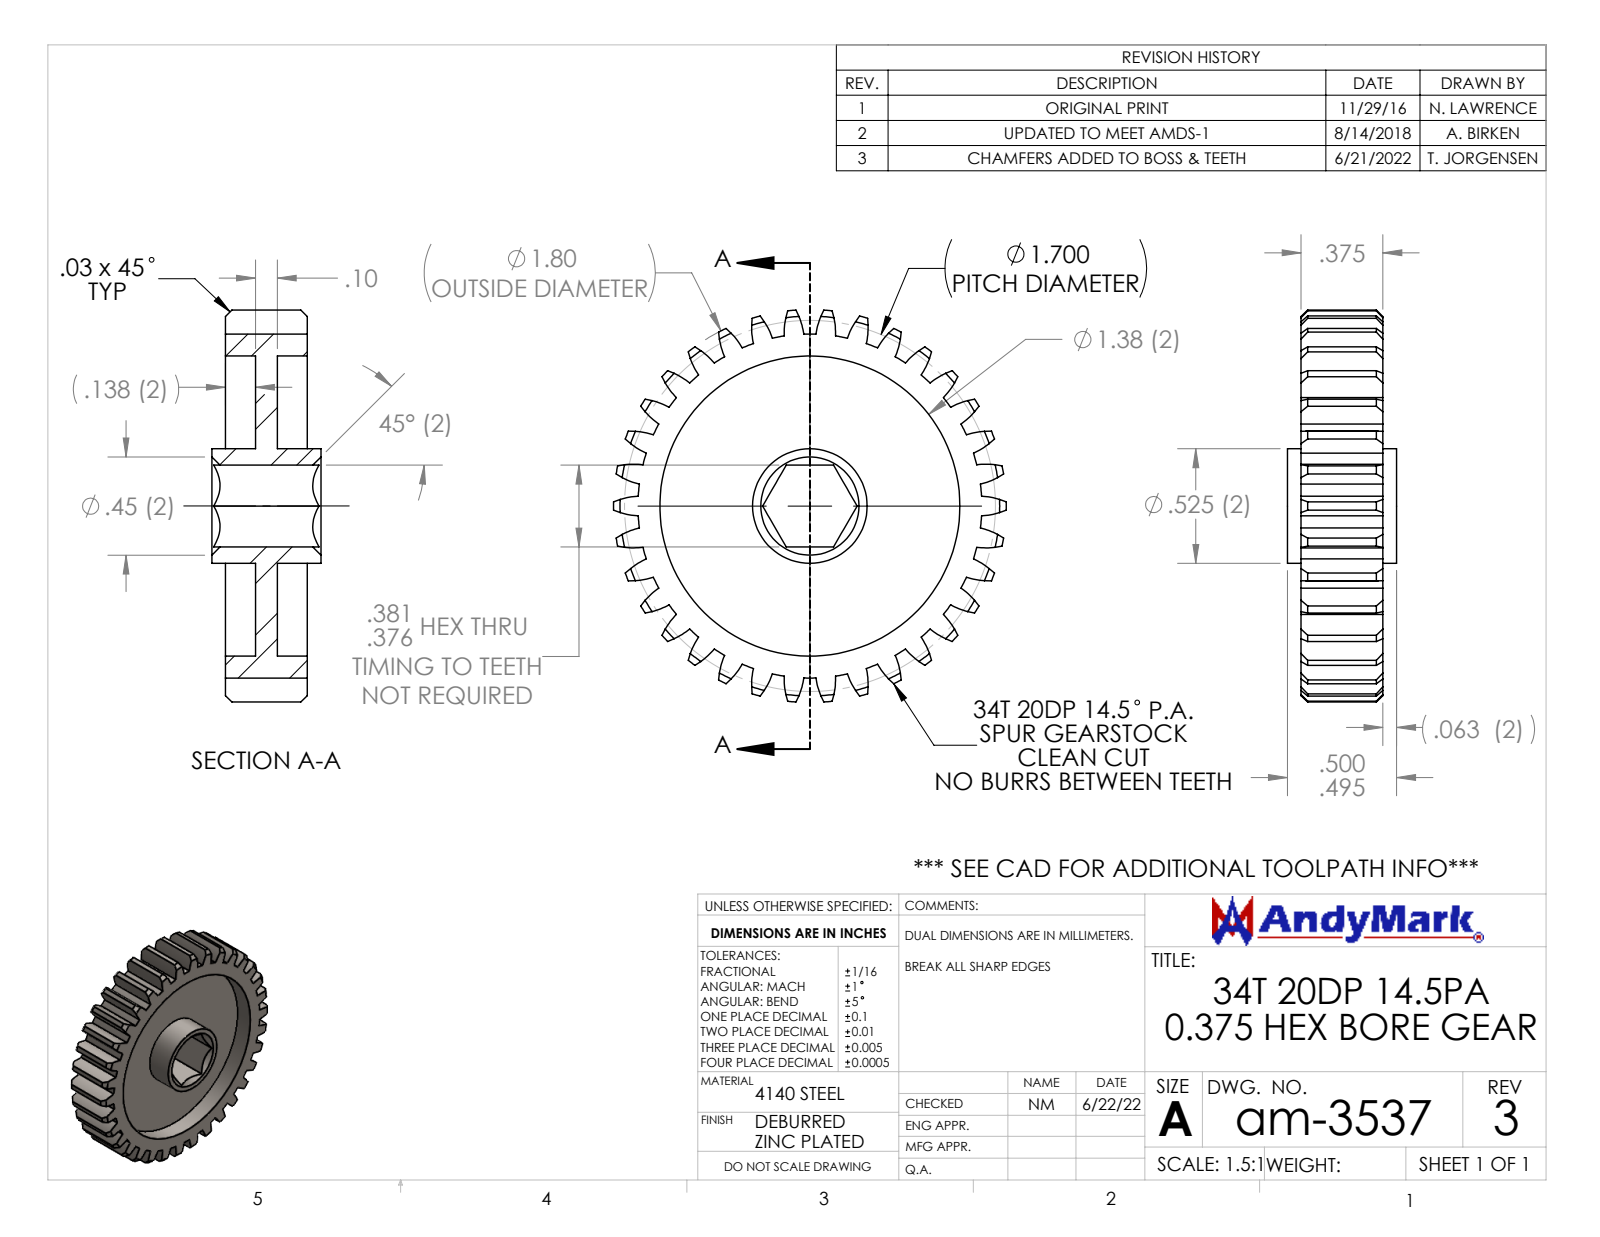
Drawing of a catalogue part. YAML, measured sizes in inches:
part_name: "am-3537 34T 20DP 375hex 375 FW"
step_written_by: "SolidWorks 2021 (CONFIG_CONTROL_DESIGN)"
units: inches
bodies: {solids: 1, faces: 233, planar: 12, cylindrical: 149, other: 72}
overall_size: [1.8, 1.795, 0.5]
volume: 0.448
surface_area: 10.72
round_holes:
  - {diameter: 1.375, count: 1}
round_bosses_or_shafts:
  - {diameter: 0.525, count: 1}
partial_cylinders:
  - {radius: 0.34, count: 68}
  - {radius: 0.788, count: 1}
  - {radius: 0.9, count: 1}
face_to_face_distances: [0.1, 0.238, 0.138, 0.137, 0.237, 0.375, 0.375, 0.2, 0.3, 0.063]
